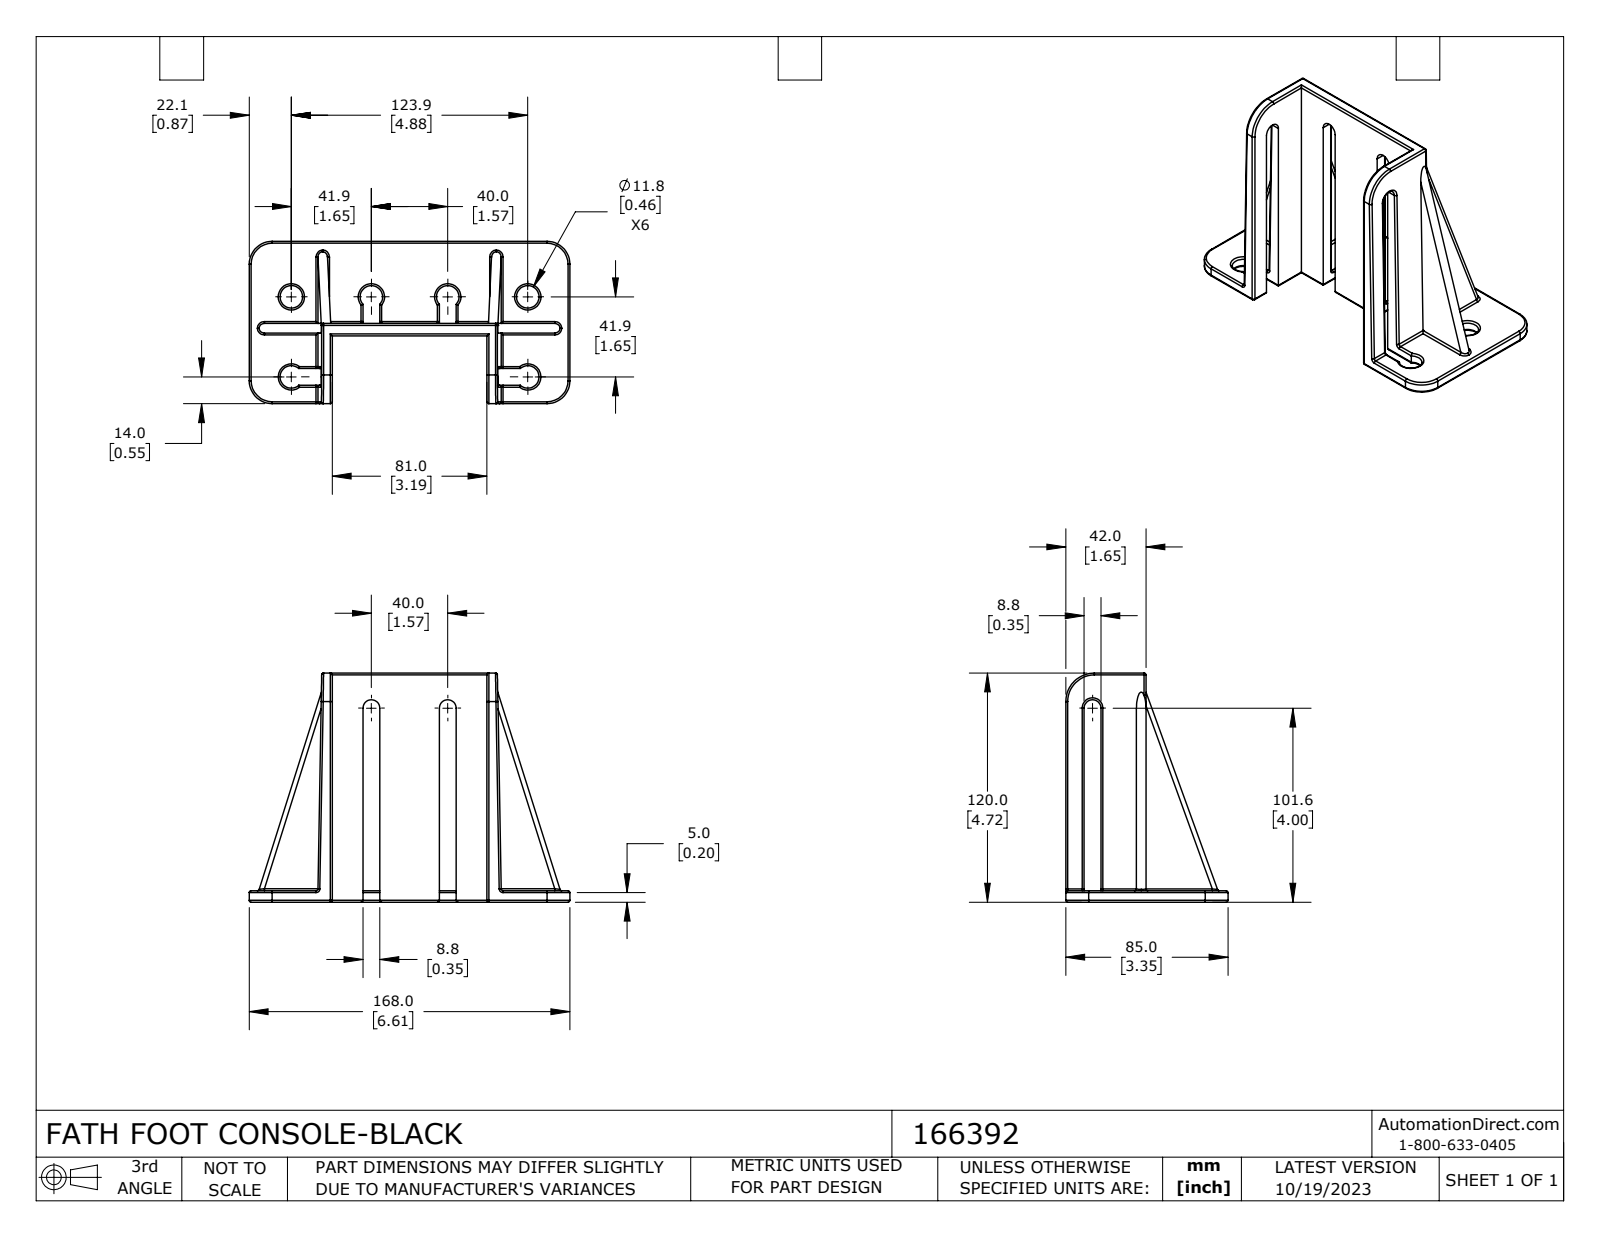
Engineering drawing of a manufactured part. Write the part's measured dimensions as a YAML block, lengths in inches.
part_name: "166392"
step_written_by: "SolidWorks 2023 (CONFIG_CONTROL_DESIGN)"
units: inches
bodies: {solids: 1, faces: 195, planar: 30, cylindrical: 97, other: 68}
overall_size: [6.614, 4.724, 3.346]
volume: 11.79
surface_area: 114.4
round_holes:
  - {diameter: 0.465, count: 2}
partial_cylinders:
  - {radius: 0.039, count: 49}
  - {radius: 0.098, count: 4}
  - {radius: 0.232, count: 4}
  - {radius: 0.472, count: 4}
  - {radius: 0.173, count: 3}
  - {radius: 0.591, count: 1}
face_to_face_distances: [0.256, 0.236, 0.197, 3.19, 0.059, 0.346, 1.02, 1.079, 1.276, 0.673]
hole_center_spacings: [4.876]
